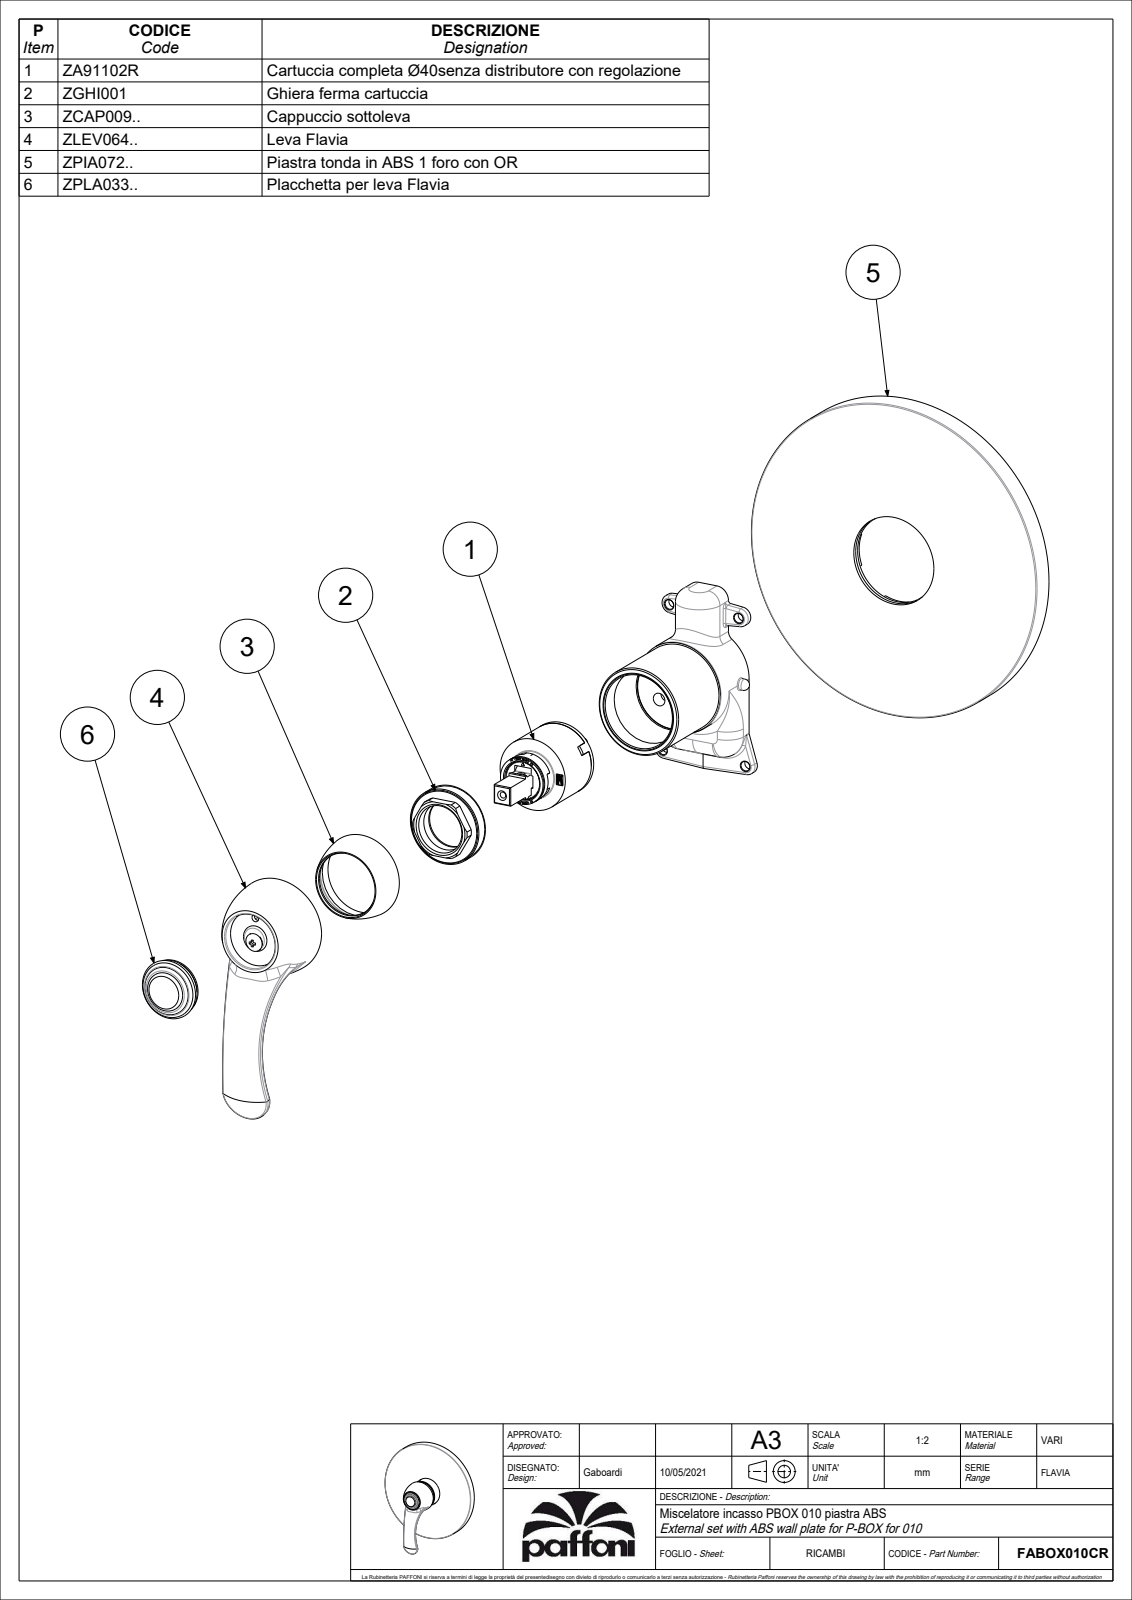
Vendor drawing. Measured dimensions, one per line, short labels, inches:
name: FABOX010CR
written by: CREO PARAMETRIC BY PTC INC, 2020044 (CONFIG_CONTROL_DESIGN)
unit: in
bodies: 2 solids, 1014 faces (596 planar, 237 cylindrical, 181 other)
size: 7.27 × 6.811 × 3.194
volume: 14.73 in³; area: 175.2 in²
holes: 2× ⌀0.157, 2× ⌀0.315, 1× ⌀0.118, 1× ⌀0.13, 1× ⌀0.197, 1× ⌀0.276, 1× ⌀0.433, 1× ⌀0.827, 1× ⌀0.835, 1× ⌀1.028, 1× ⌀1.181, 1× ⌀1.358
bosses: 1× ⌀6.811, 1× ⌀6.575, 1× ⌀2.224, 1× ⌀1.894, 1× ⌀1.555, 1× ⌀1.445, 1× ⌀1.299, 1× ⌀1.177
rounds: 26× R0.02, 24× R0.008, 4× R0.059, 1× R0.276, 1× R0.396, 1× R0.469, 1× R0.484, 1× R0.974
face distances: 0.512, 0.433, 0.079, 0.256, 0.098, 0.11, 0.323, 0.402, 2.386, 2.276
hole spacings: 0.351, 0.39, 0.394, 0.581, 0.78, 0.058, 0.064, 0.218
